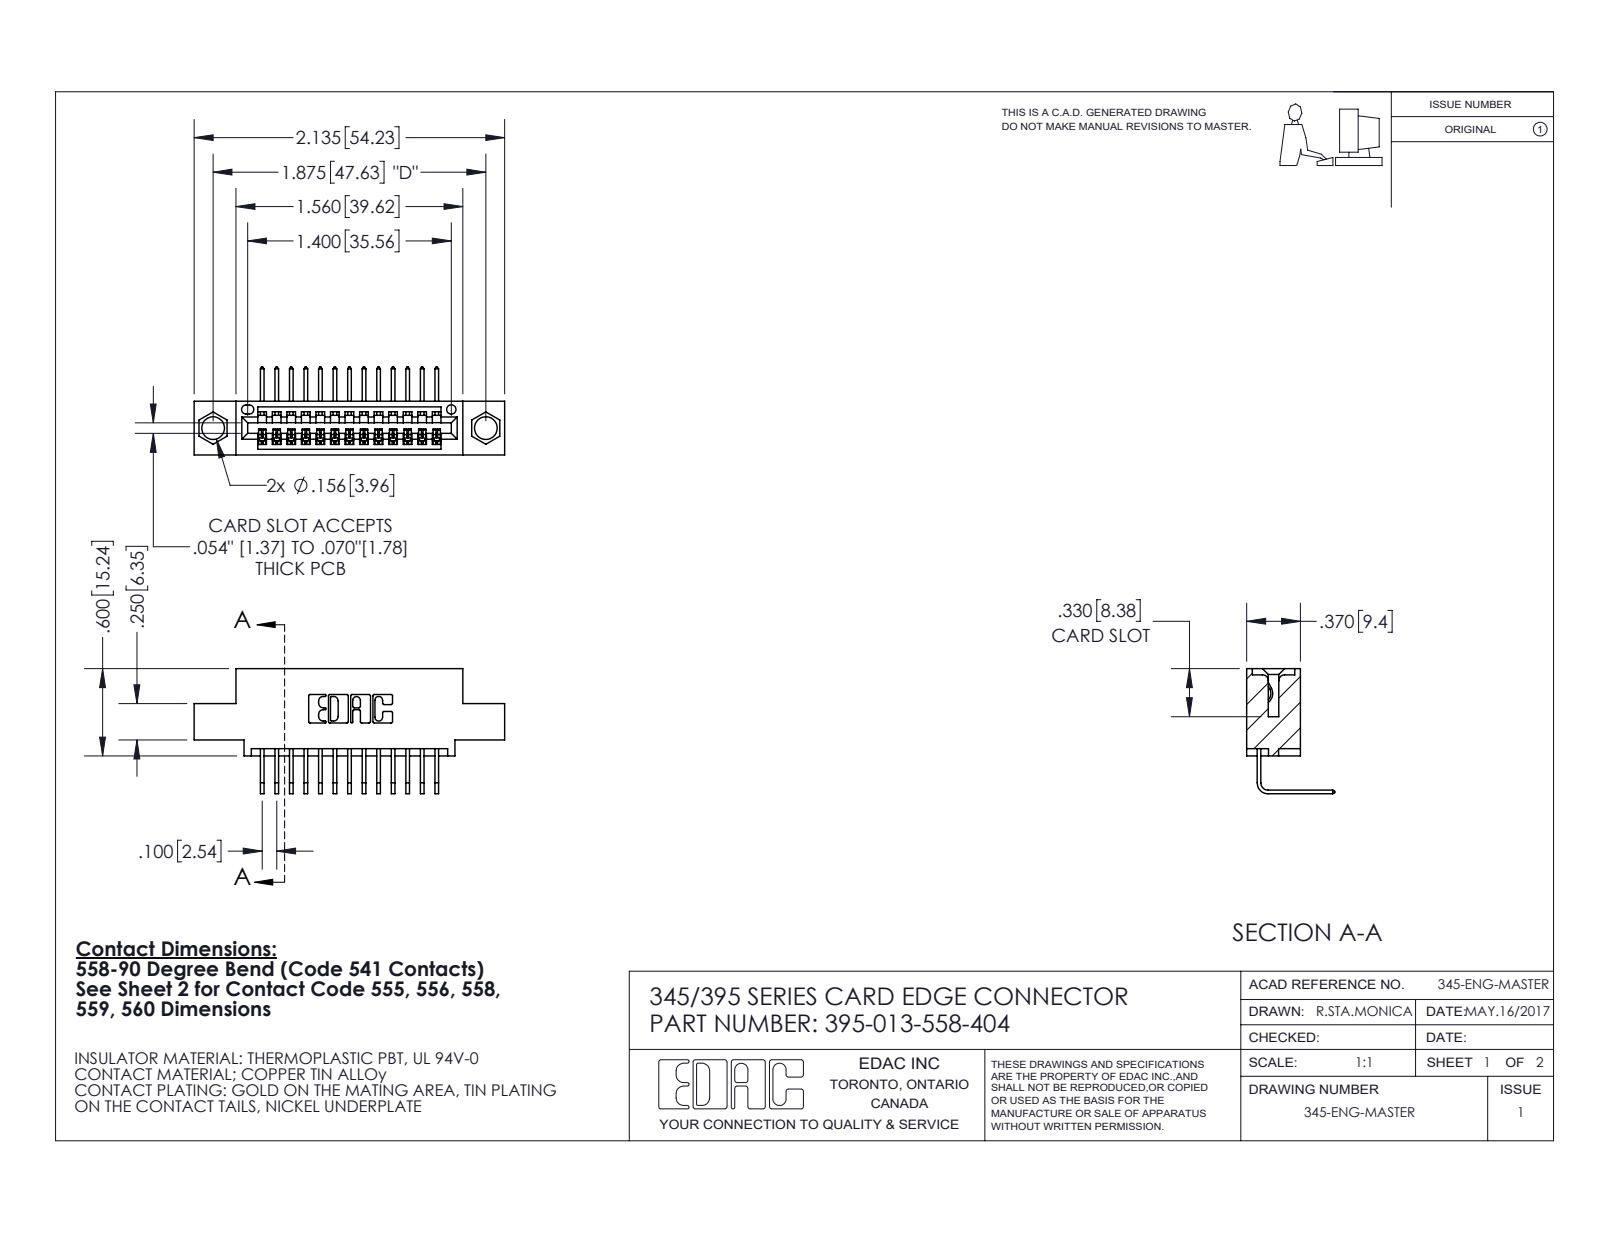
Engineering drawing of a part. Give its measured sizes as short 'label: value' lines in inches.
name: 345 Part_0.110 Offset - 0.156 Dia-TI; 345-292-001_558 Tail - 2; 395-013-558-404
written by: SolidWorks 2020 (CONFIG_CONTROL_DESIGN)
unit: in
bodies: 14 solids, 924 faces (644 planar, 280 cylindrical, 0 other)
size: 2.135 × 0.859 × 0.605
volume: 0.292 in³; area: 9.506 in²
holes: 2× ⌀0.156, 1× ⌀0.064
rounds: 26× R0.006, 22× R0.01, 6× R0.007, 6× R0.031, 3× R0.026, 2× R0.031, 2× R0.04, 1× R0.014
face distances: 0.072, 0.298, 0.2, 0.37, 0.098, 0.272, 0.025, 0.1, 0.225, 0.16
hole spacings: 0.27, 1.643, 1.875
